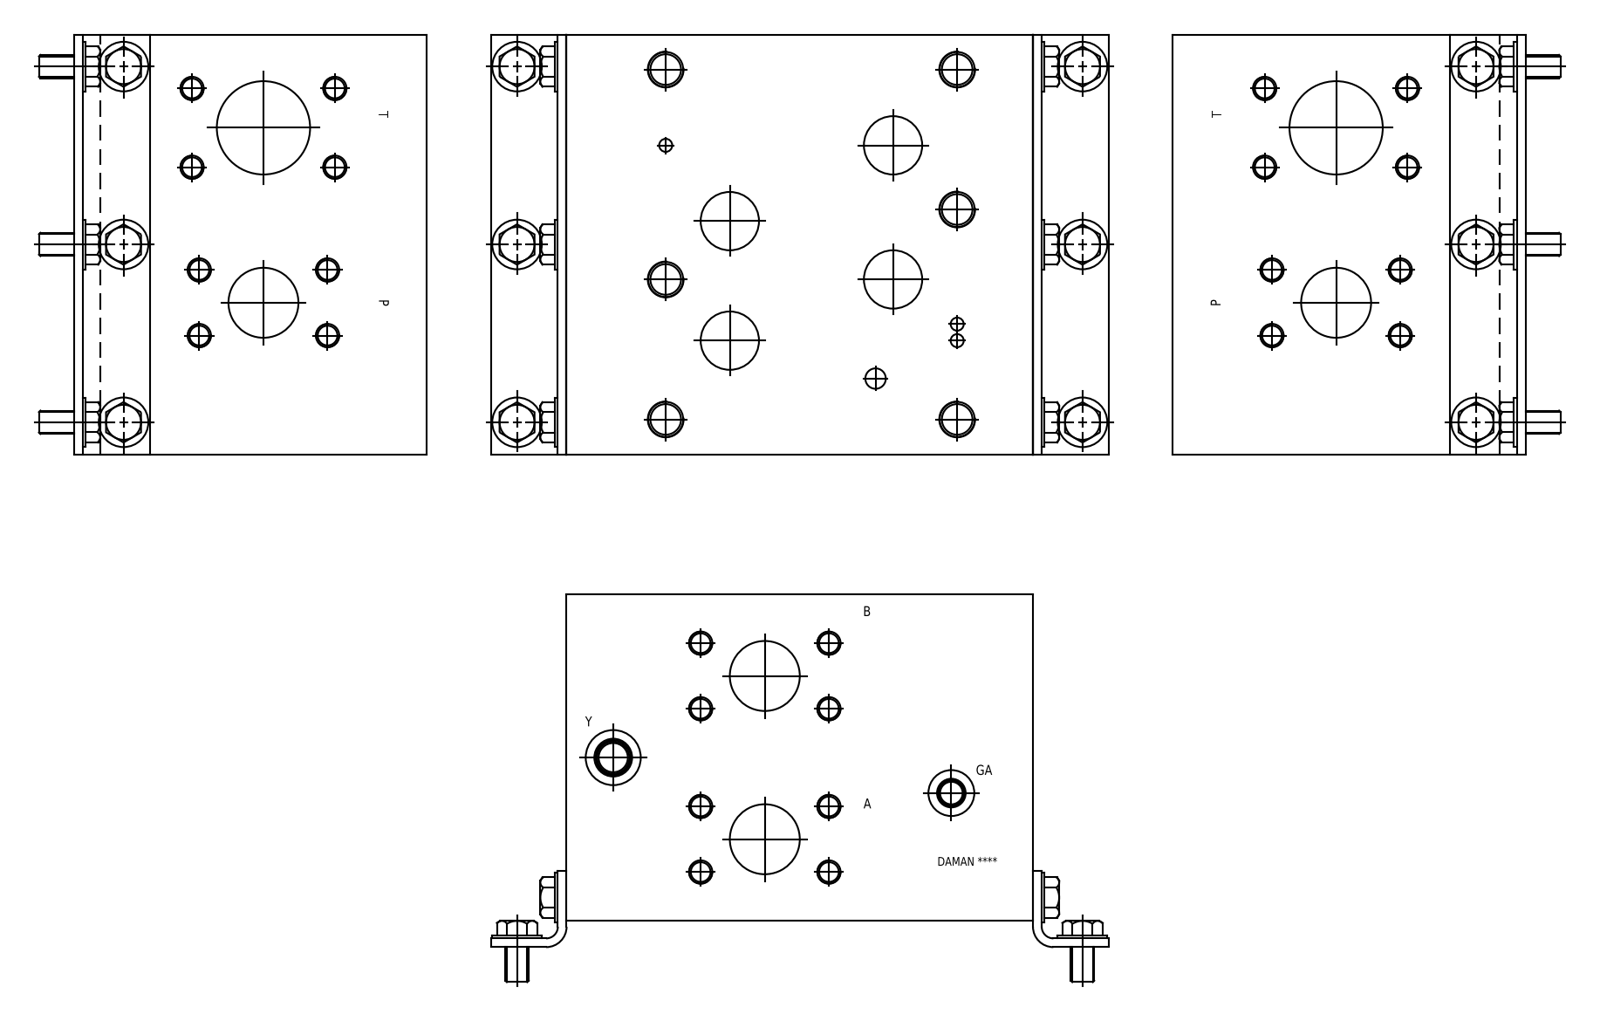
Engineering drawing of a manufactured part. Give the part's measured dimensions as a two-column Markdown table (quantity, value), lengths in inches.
| quantity | value |
| --- | --- |
| part name | Part_DD10P019F_3D |
| STEP written by | Autodesk Inventor 2019 (AUTOMOTIVE_DESIGN) |
| units | inches |
| bodies | 1 solid, 621 faces (354 planar, 96 cylindrical, 171 other) |
| overall size | 10 × 9 × 7 |
| volume | 605.4 in³ |
| surface area | 563.7 in² |
| round holes (diameter × count) | 0.422 × 19, 0.5 × 19, 0.75 × 7, 0.656 × 6, 1.25 × 4, 0.281 × 3, 1.5 × 3, 0.437 × 1, 0.484 × 1, 0.508 × 1, 0.562 × 1, 0.572 × 1 |
| main face-to-face distances | 7, 9, 10, 0.031, 8.969, 1.19, 8.81, 5.38, 1.62, 7.62 |
| hole center spacings | 1.406, 1.544, 1.544, 2.75, 3.089, 3.5, 1.748, 3.117 |
